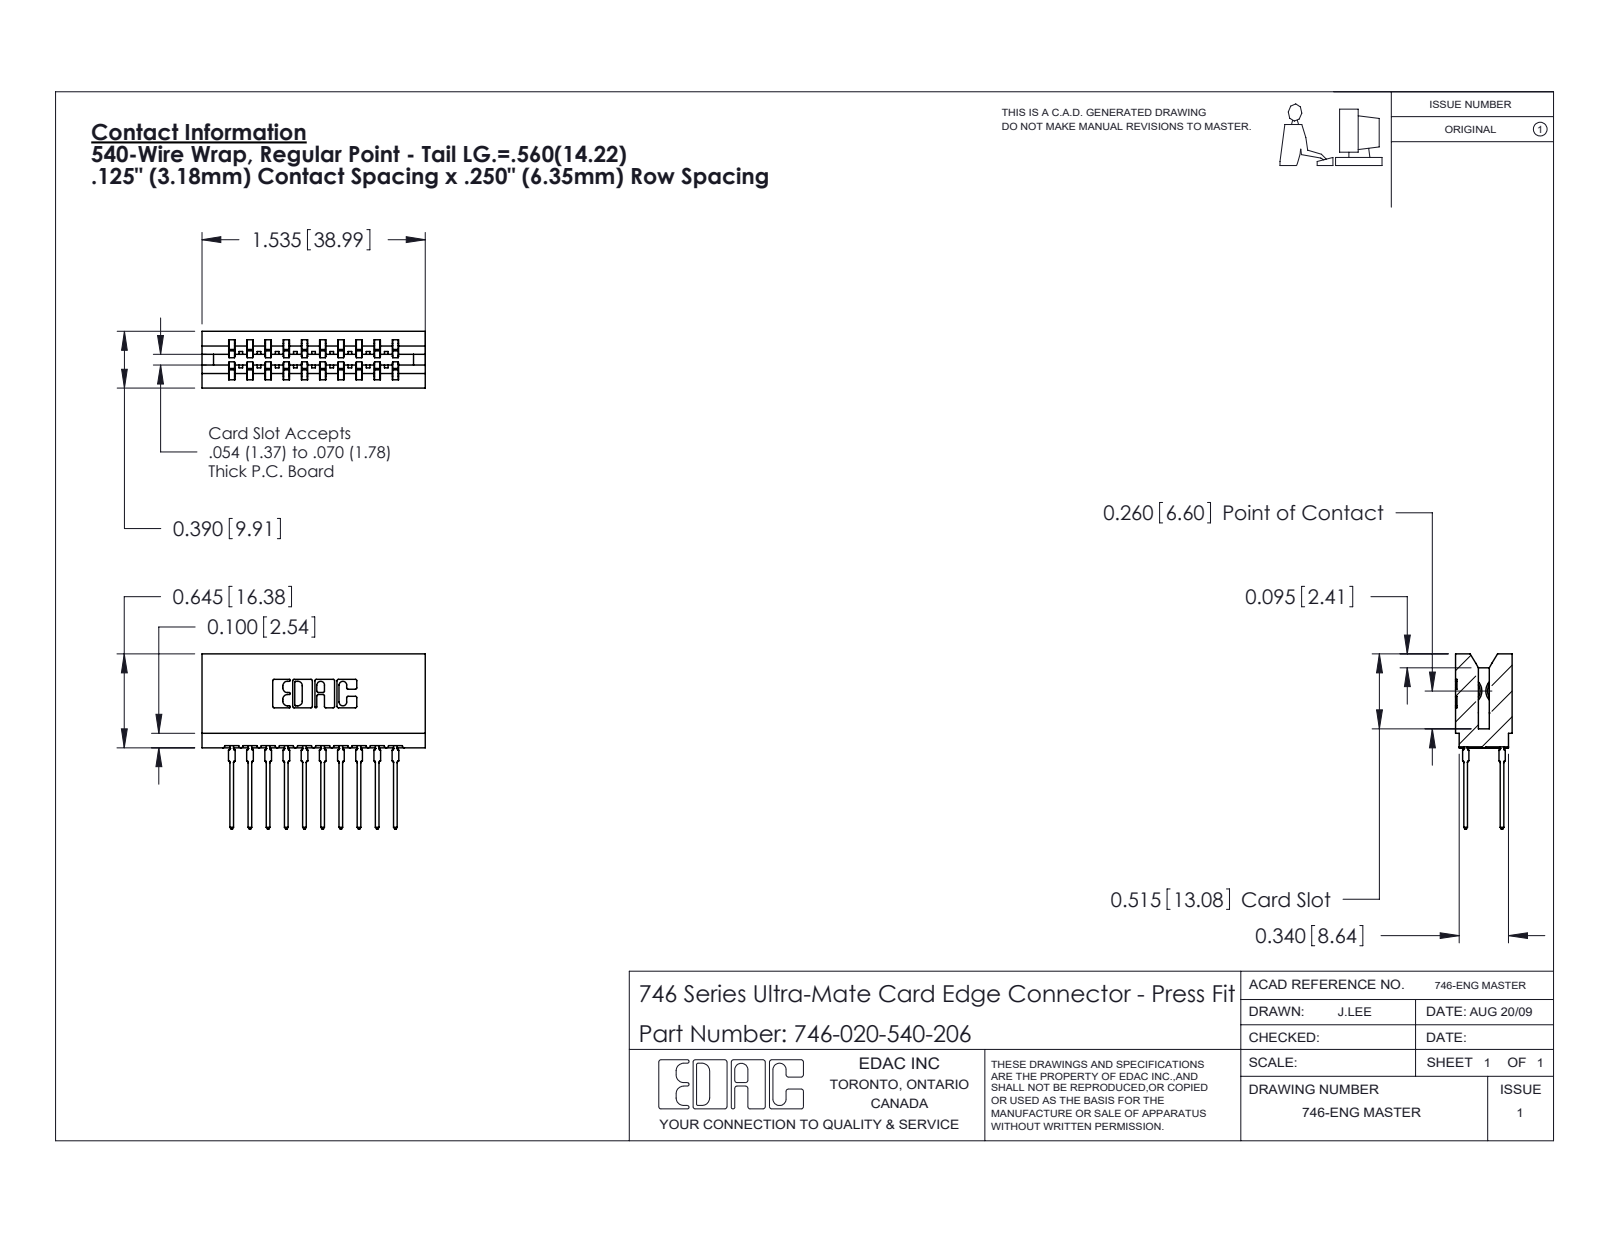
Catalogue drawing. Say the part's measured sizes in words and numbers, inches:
The part is named "746-020-540-206; 746-292-001_540; 746 Part_.515 Slot Depth - 06". Its 3-D file was written by "SolidWorks 2020 (CONFIG_CONTROL_DESIGN)". It is 21 solids with 1888 faces: 976 planar, 392 cylindrical and 520 other. Overall it measures 1.535 by 1.204 by 0.39 inches. Its volume is 0.27 cubic inches and its surface area 10.48 square inches. Partial cylindrical surfaces (rounded edges, fillets, slot ends): 40 of radius 0.021, 22 of radius 0.01, 11 of radius 0.015, 8 of radius 0.005, 8 of radius 0.011, 6 of radius 0.007, 6 of radius 0.031, 3 of radius 0.026. The main face-to-face distances are 0.25, 0.333, 0.057, 0.5, 0.042, 0.125, 0.292, 0.75, 0.083, 0.39.
